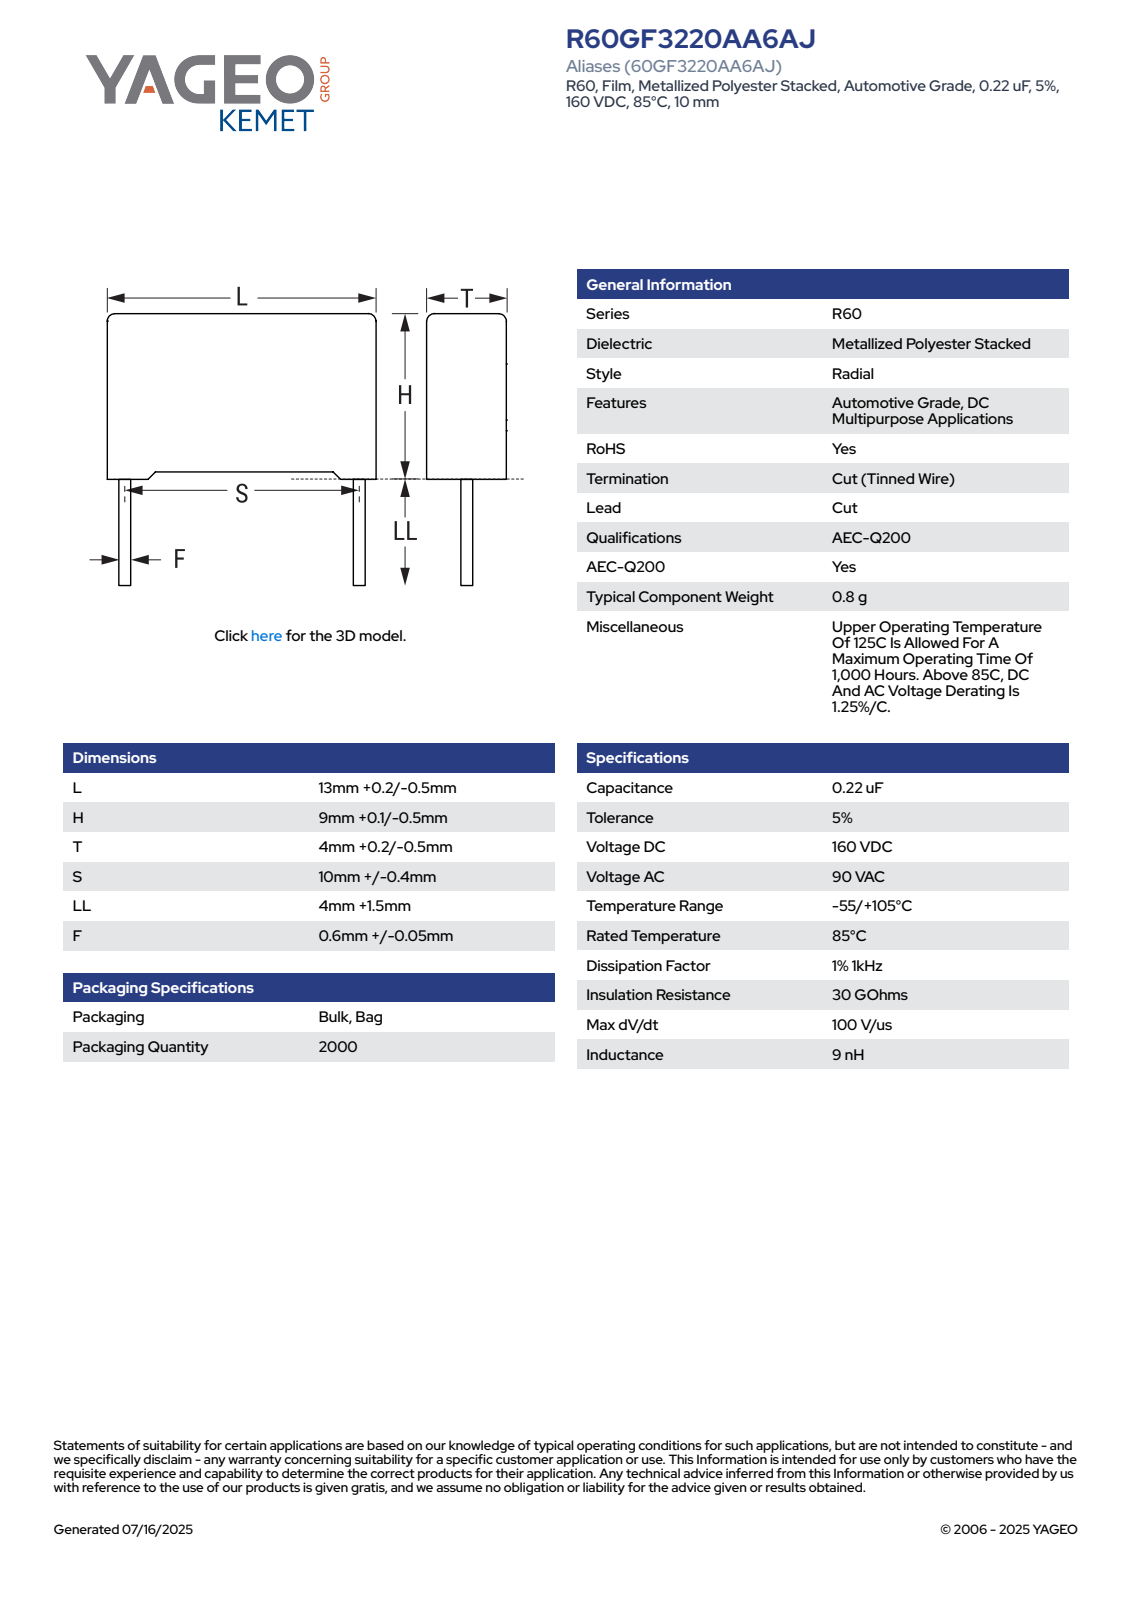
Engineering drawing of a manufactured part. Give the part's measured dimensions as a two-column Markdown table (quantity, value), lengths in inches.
| quantity | value |
| --- | --- |
| part name | CFR_RB2_13X9X4_L13.2H9.1T4.2S10LL5.5F0.65 |
| STEP written by | SolidWorks 2021 (AUTOMOTIVE_DESIGN) |
| units | inches |
| bodies | 4 solids, 85 faces (77 planar, 8 cylindrical, 0 other) |
| overall size | 0.575 × 0.52 × 0.166 |
| volume | 0.029 in³ |
| surface area | 0.735 in² |
| round bosses / shafts (diameter × count) | 0.026 × 2 |
| partial cylindrical surfaces (radius × count) | 0.02 × 4 |
| main face-to-face distances | 0.165, 0.329, 0.52, 0.017, 0.148, 0.03, 0.358, 0.131, 0.012, 0.346 |
